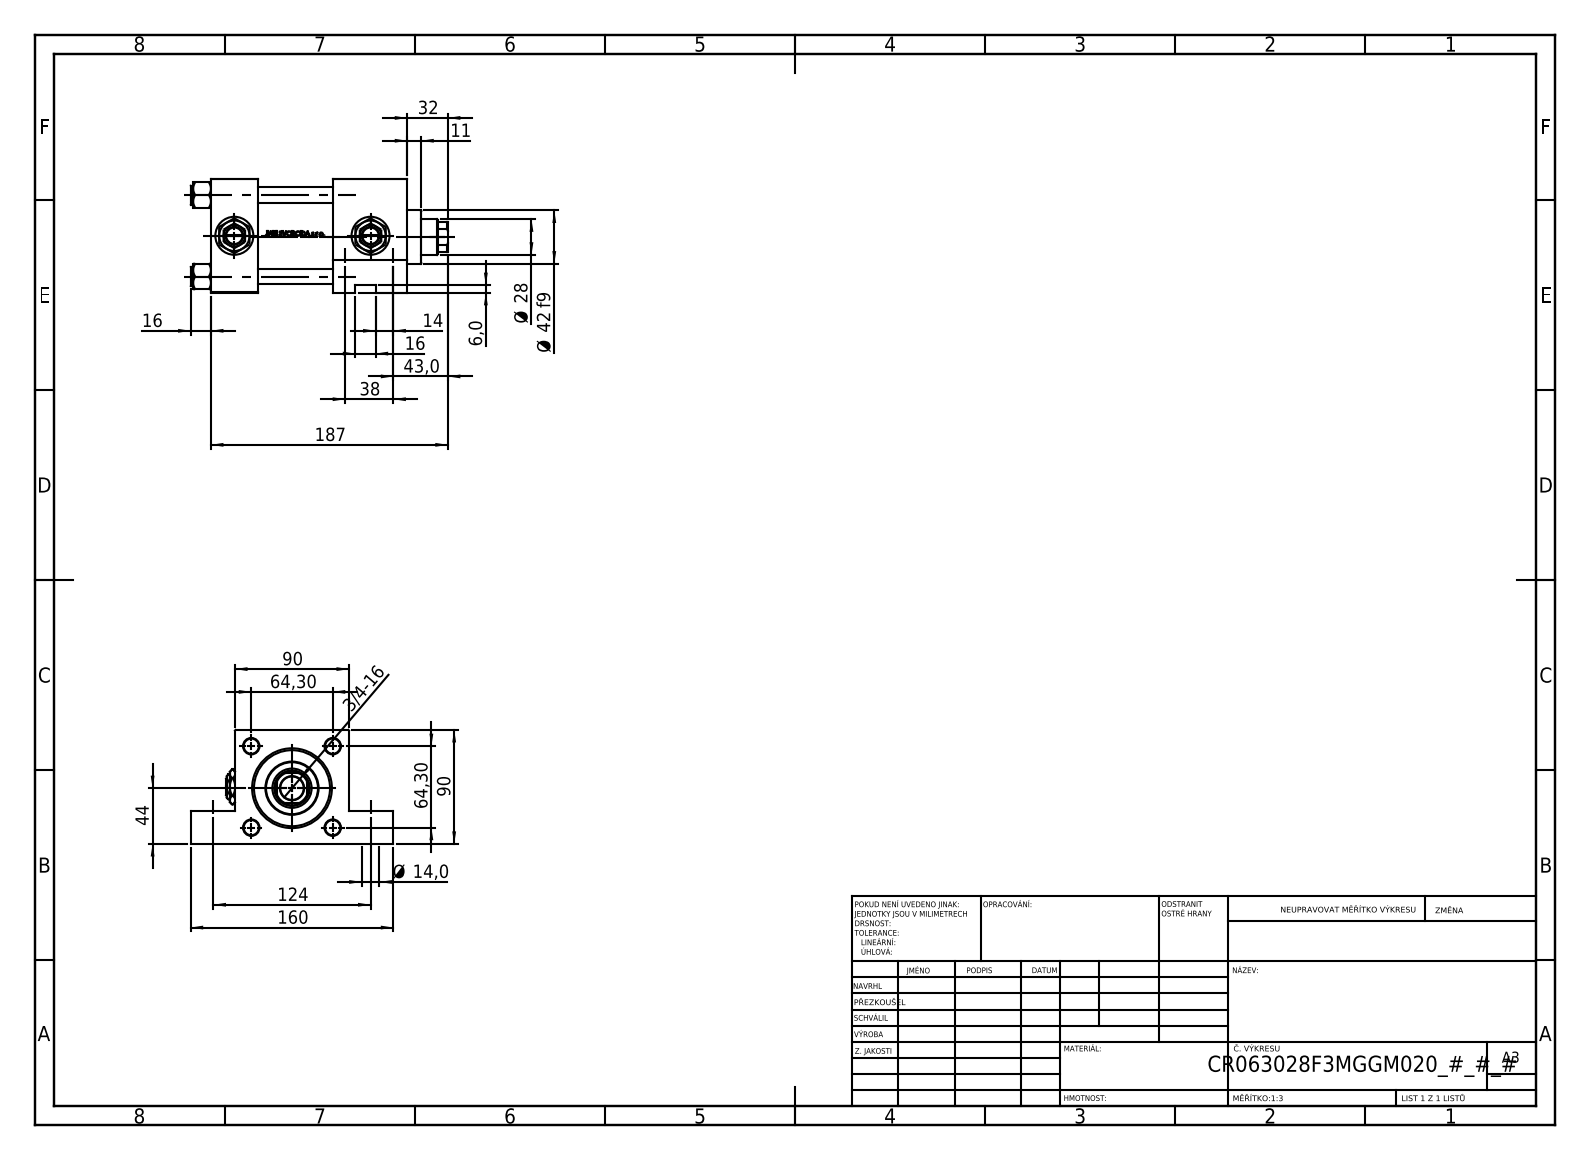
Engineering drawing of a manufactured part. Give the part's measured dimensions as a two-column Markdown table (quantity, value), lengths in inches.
| quantity | value |
| --- | --- |
| part name | Zatka_pro_OIL_PORT; V215_VC_A; NUT_M5_F; V215CR_F_Body (+2 more) |
| STEP written by | SolidWorks 2019 (CONFIG_CONTROL_DESIGN) |
| units | inches |
| bodies | 13 solids, 1203 faces (485 planar, 136 cylindrical, 582 other) |
| overall size | 7.992 × 6.299 × 3.543 |
| volume | 62.37 in³ |
| surface area | 308.1 in² |
| round holes (diameter × count) | 0.472 × 4, 0.825 × 4, 1.181 × 4, 0.276 × 3, 0.551 × 2, 0.551 × 2, 0.728 × 1, 1.102 × 1, 1.22 × 1, 1.969 × 1, 2.362 × 1, 2.48 × 1 |
| round bosses / shafts (diameter × count) | 0.591 × 4, 2.717 × 1, 1.654 × 1 |
| partial cylindrical surfaces (radius × count) | 0.531 × 1 |
| main face-to-face distances | 3.543, 2.323, 1.457, 6.102, 4.646, 3.78, 0.787, 2.52, 1.024, 4.921 |
| hole center spacings | 2.531, 1.496, 1.763, 1.818, 2.472, 2.678, 3.58, 4.222 |
